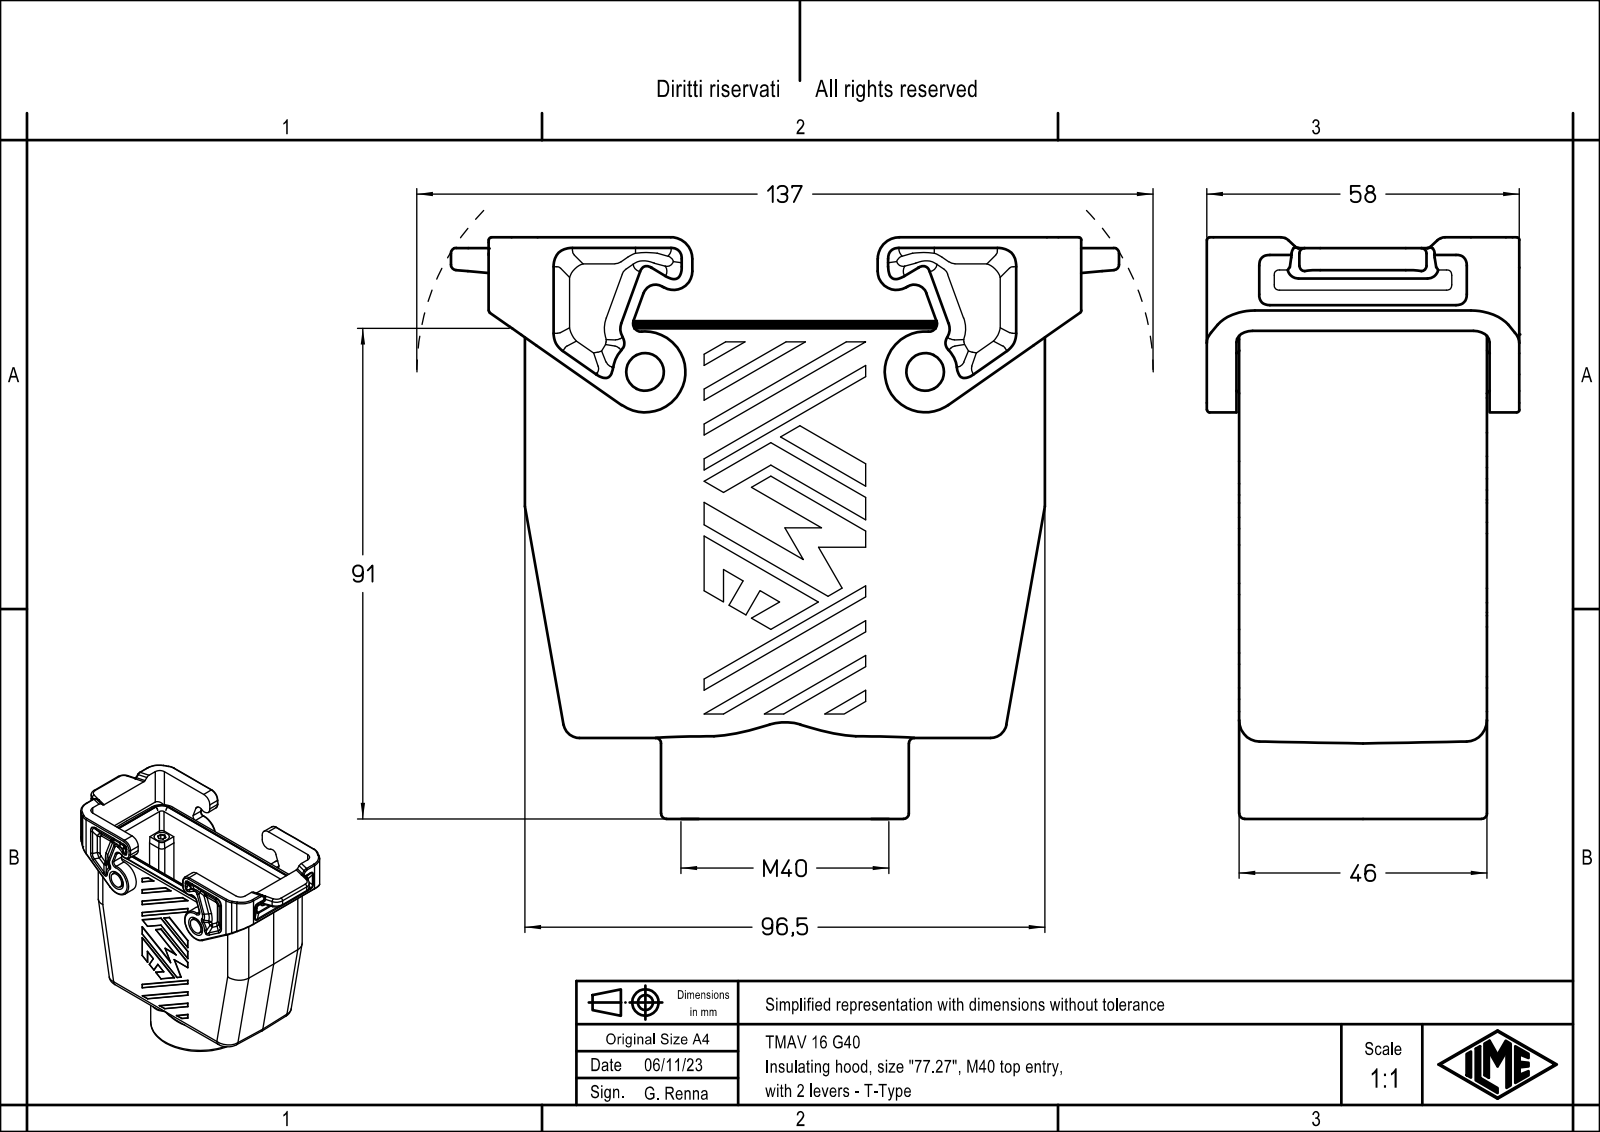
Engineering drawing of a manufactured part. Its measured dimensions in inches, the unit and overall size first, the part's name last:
Units: inches
Overall size (bounding box): 4.882 × 4.248 × 2.283
Round holes (diameter × count): ⌀1.339 ×1, ⌀1.52 ×1
Round bosses / shafts (diameter × count): ⌀0.276 ×2, ⌀1.811 ×1
Partial cylindrical surfaces — rounded edges, fillets, slot ends (radius × count): R0.006 ×88, R0.118 ×20, R0.039 ×16, R0.079 ×16, R0.059 ×10, R0.051 ×8, R0.236 ×8, R0.276 ×8
Main face-to-face distances: 0.213, 1.598, 1.386, 1.811, 0.02, 0.232, 1.618, 1.831, 0.217, 0.236
Volume: 9.334 in³ · Surface area: 94.04 in²
Bodies: 1 solid, 562 faces (218 planar, 282 cylindrical, 62 other)
Part name (STEP PRODUCT): TMAV 16 G40
STEP written by: Creo Elements/Direct Modeling 20.1B 02-Apr-2019 (C) Parametric Technology GmbH (AUTOMOTIVE_DESIGN)
